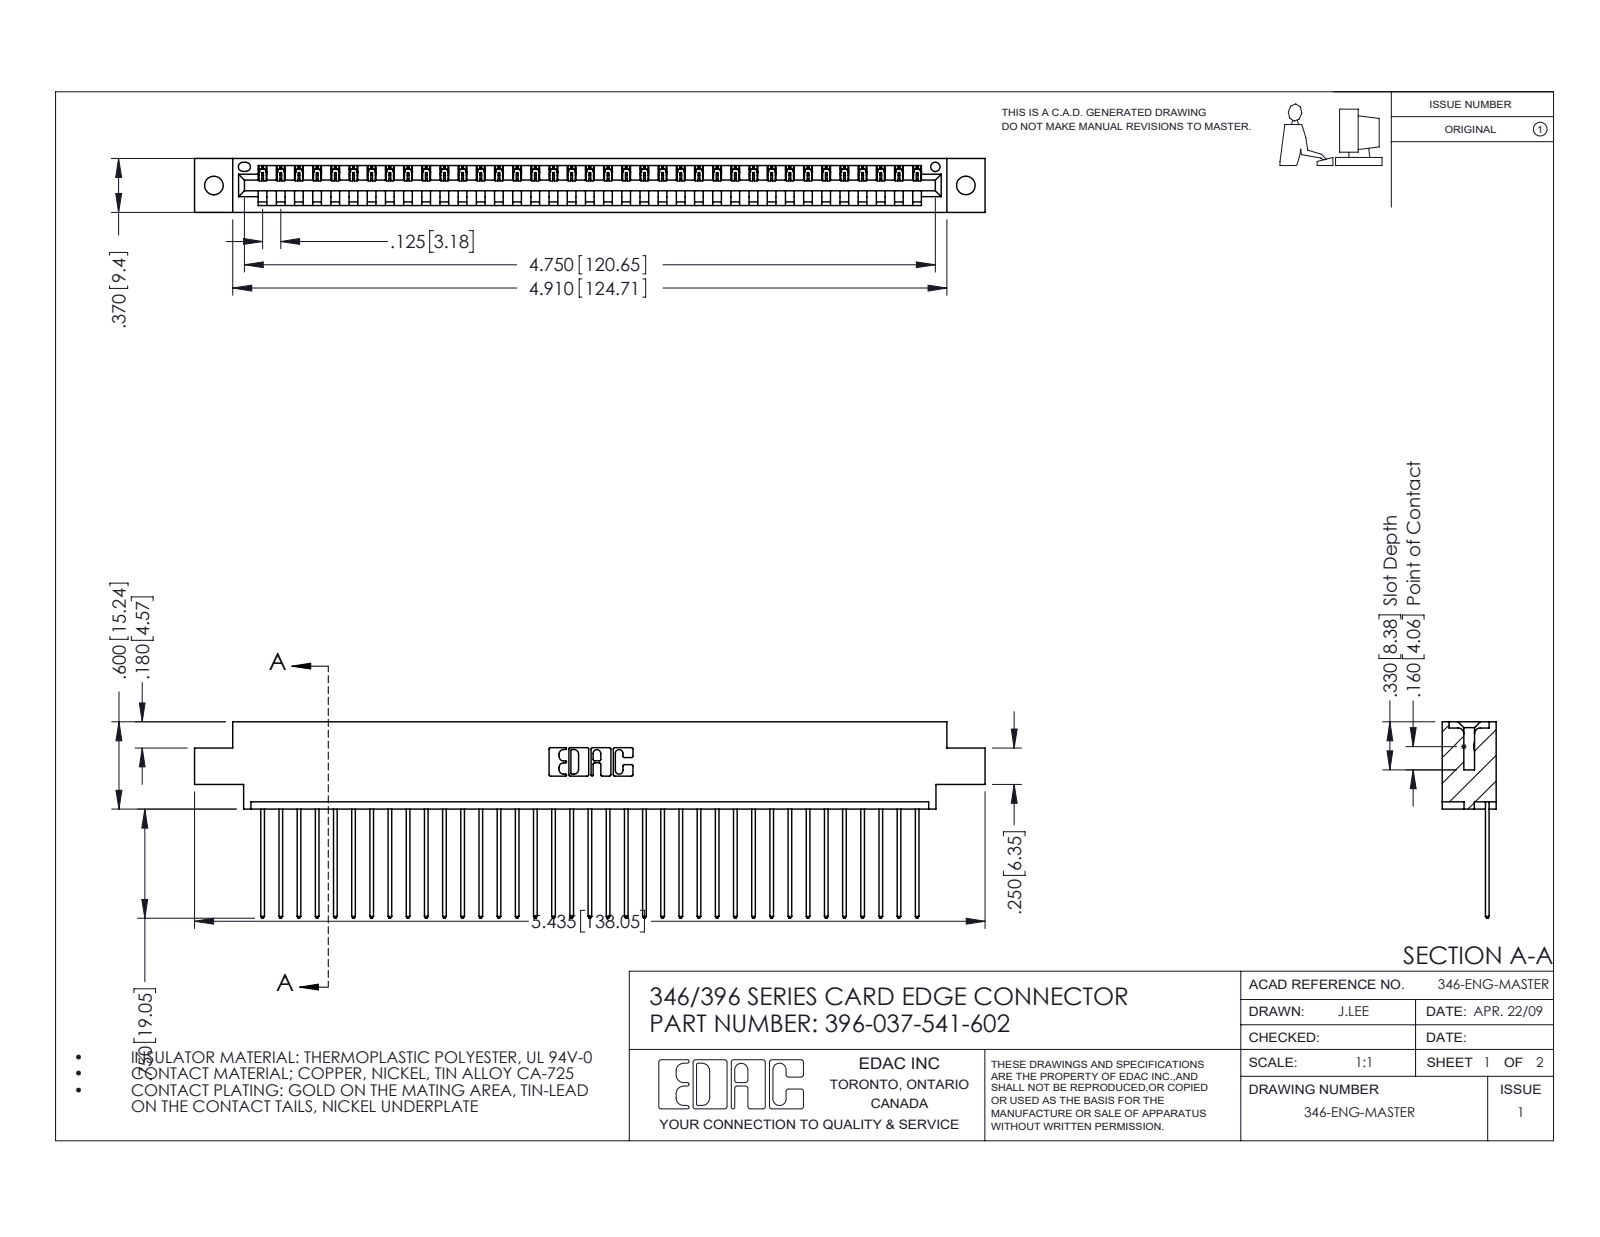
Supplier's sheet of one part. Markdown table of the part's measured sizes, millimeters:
| quantity | value |
| --- | --- |
| part name | 345-292-001_345-293-141; 346 Part_0.170 Offset - 0.128 Dia; 396-037-541-602 |
| STEP written by | SolidWorks 2016 (CONFIG_CONTROL_DESIGN) |
| units | millimeters |
| bodies | 38 solids, 2272 faces (1560 planar, 712 cylindrical, 0 other) |
| overall size | 138 × 34.3 × 9.4 |
| volume | 13 100 mm³ |
| surface area | 16 950 mm² |
| round holes (diameter × count) | 3.3 × 2, 1.6 × 1 |
| partial cylindrical surfaces (radius × count) | 0.2 × 74, 0.3 × 74, 0.3 × 22, 0.2 × 6, 0.8 × 6, 0.7 × 3, 0.8 × 2, 1 × 2 |
| main face-to-face distances | 1.2, 8.2, 9.4, 6.4, 1.8, 7.6, 0.6, 3.8, 5.6, 2.5 |
| hole center spacings | 6.2, 126, 131.3 |
